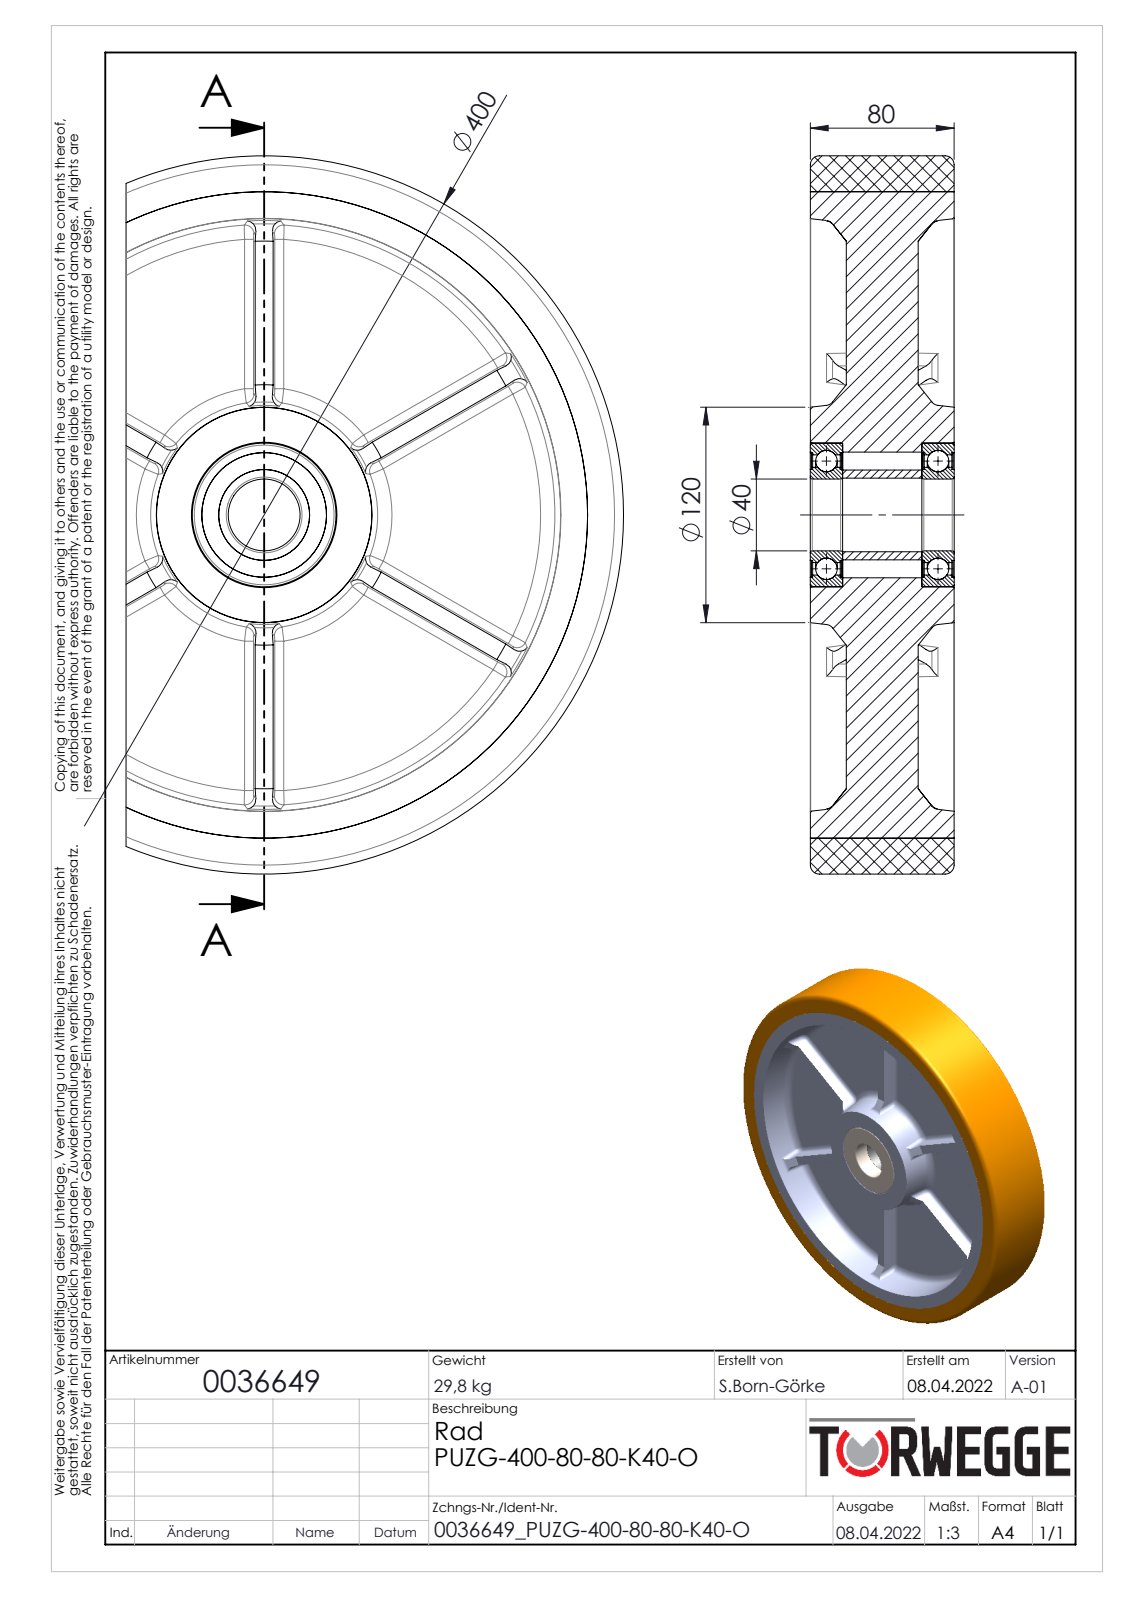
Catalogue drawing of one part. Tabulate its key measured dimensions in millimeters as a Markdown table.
| quantity | value |
| --- | --- |
| part name | 0036649 |
| STEP written by | SolidWorks 2020 (AUTOMOTIVE_DESIGN) |
| units | millimeters |
| bodies | 13 solids, 410 faces (82 planar, 96 cylindrical, 232 other) |
| overall size | 400 × 400 × 80.1 |
| volume | 5 093 000 mm³ |
| surface area | 723 977 mm² |
| round holes (diameter × count) | 40 × 1, 41 × 1, 50.6 × 1, 66.96 × 1, 69.4 × 1, 70 × 1, 80 × 1, 360 × 1 |
| round bosses / shafts (diameter × count) | 400 × 1, 53.04 × 1, 50 × 1 |
| partial cylindrical surfaces (radius × count) | 5 × 16 |
| main face-to-face distances | 35, 45, 10, 80, 13.44, 62.1, 62.05, 20, 60, 15 |
